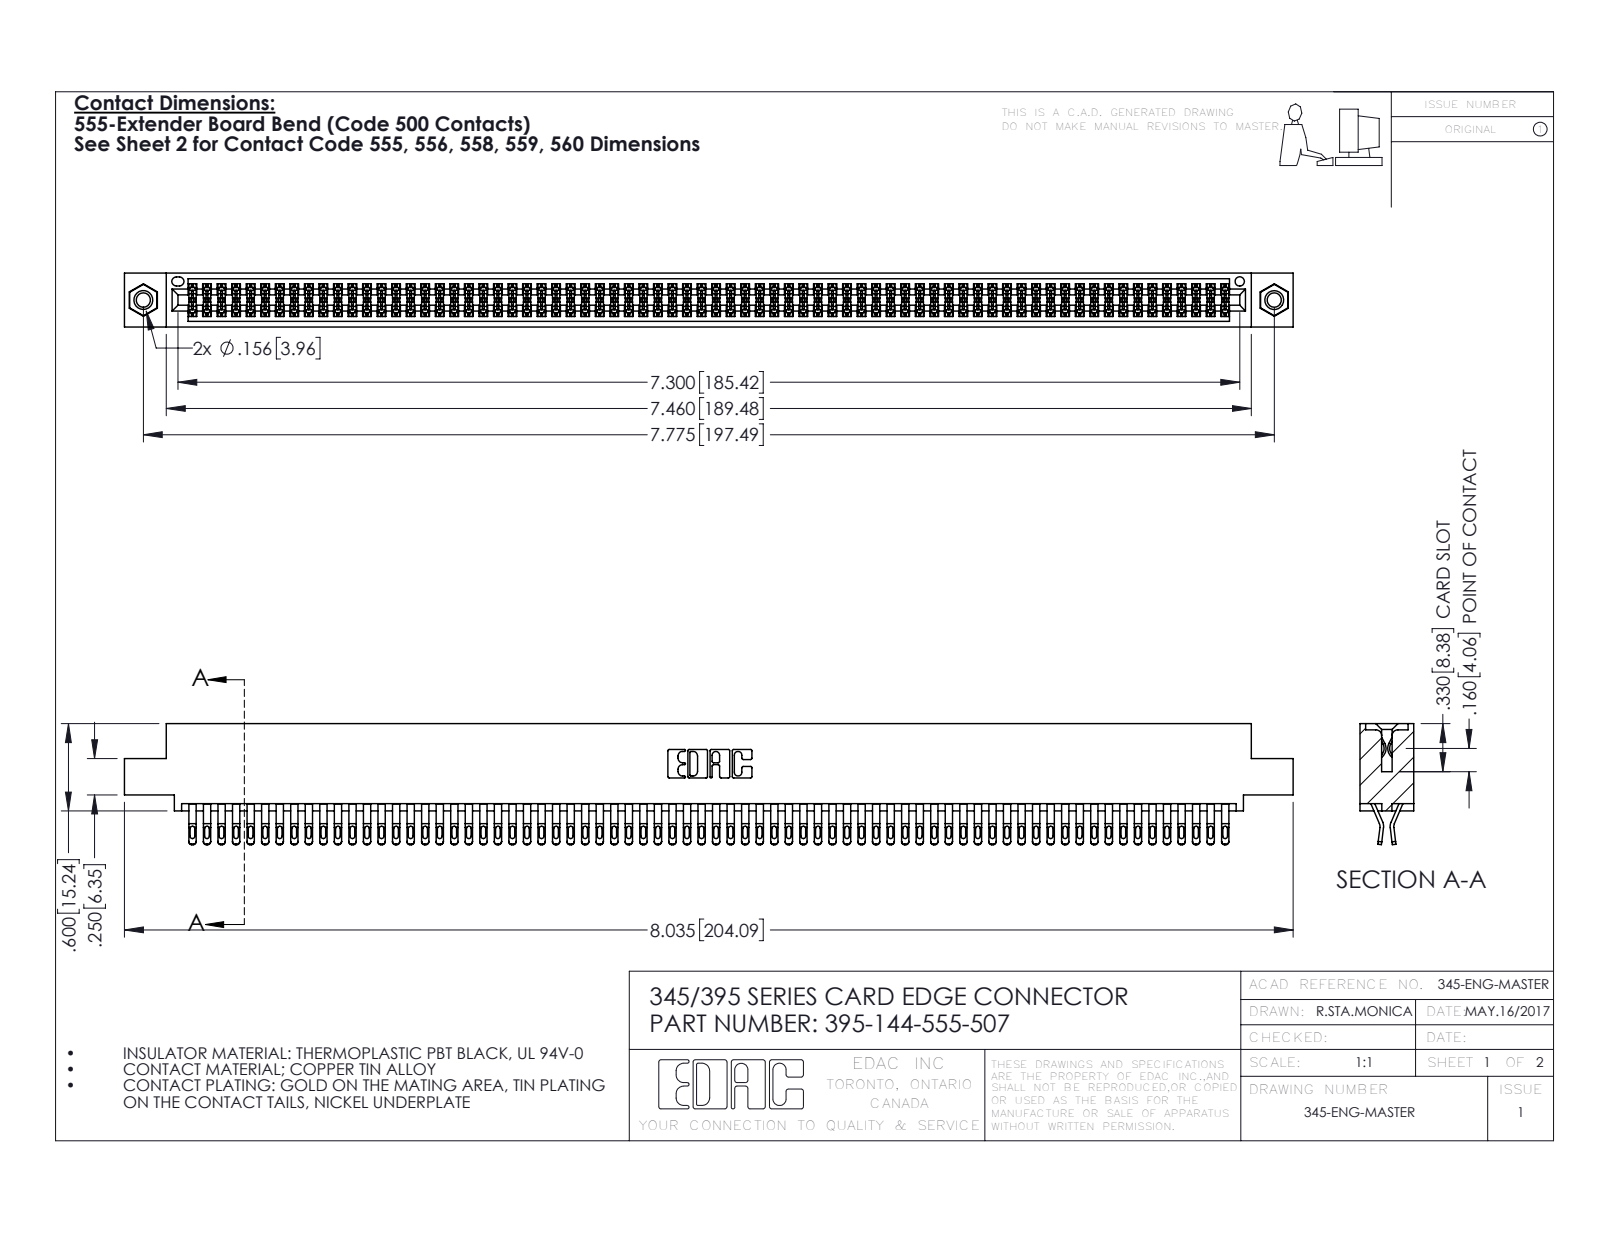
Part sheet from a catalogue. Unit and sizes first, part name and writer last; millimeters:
Units: millimetres
Overall size (bounding box): 204.1 × 21.1 × 9.4
Round holes (diameter × count): ⌀2.5 ×2, ⌀3.2 ×2, ⌀4 ×2, ⌀1.6 ×1
Round bosses / shafts (diameter × count): ⌀3.9 ×2
Partial cylindrical surfaces — rounded edges, fillets, slot ends (radius × count): R0.4 ×360, R0.5 ×288, R0.2 ×216, R0.3 ×22, R0.2 ×6, R0.8 ×6, R0.7 ×3, R0.3 ×2
Main face-to-face distances: 1.8, 7.6, 0.6, 9.4, 5.1, 2.5, 6.9, 5.7, 4.4, 3.8
Hole centre spacings: 6.9, 191.5, 197.5
Volume: 20 430 mm³ · Surface area: 32 360 mm²
Bodies: 147 solids, 8254 faces (4580 planar, 3658 cylindrical, 16 other)
Part name (STEP PRODUCT): 395-144-555-507; 345-292-001_555 Tail; 345 Part_0.110 Offset - 0.156 Dia-TI; 345-250-001_345-250-005-103
STEP written by: SolidWorks 2016 (CONFIG_CONTROL_DESIGN)
